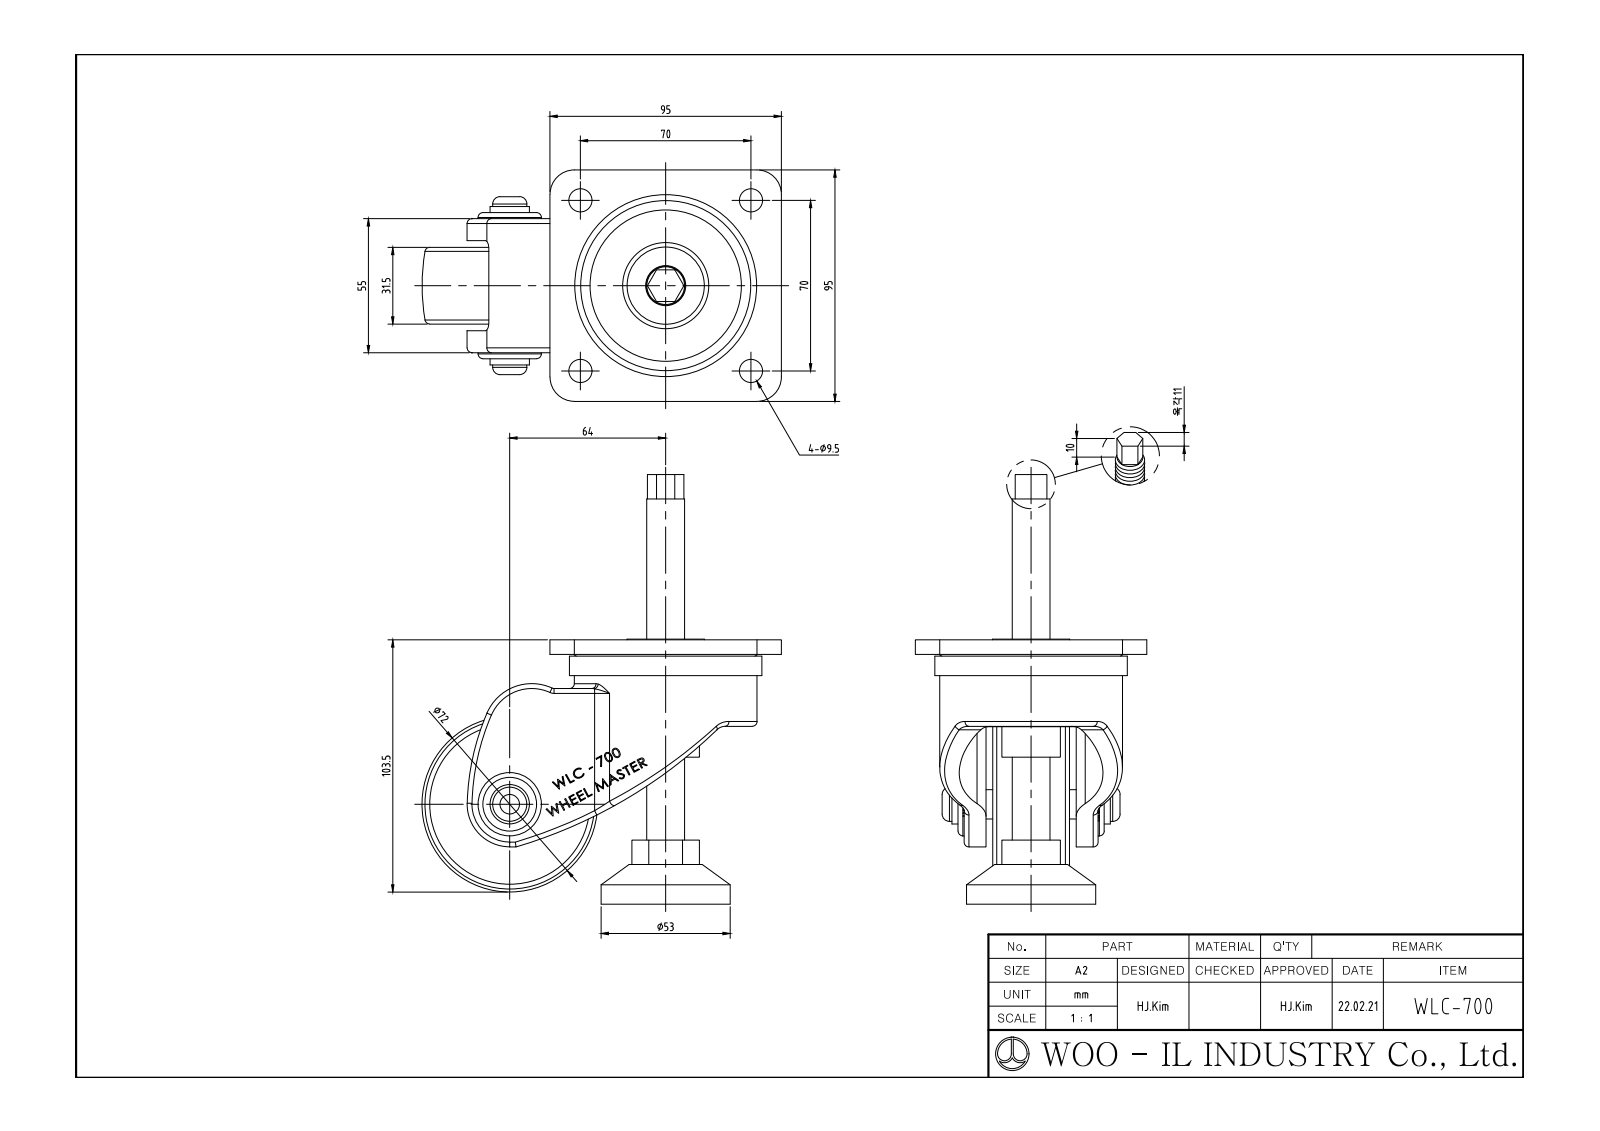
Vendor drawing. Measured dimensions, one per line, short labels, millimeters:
name: WLC-700F
written by: SolidWorks 2019 (AUTOMOTIVE_DESIGN)
unit: mm
bodies: 1 solid, 577 faces (3 planar, 6 cylindrical, 568 other)
size: 176.3 × 147.5 × 95
volume: 441 014 mm³; area: 79 003 mm²
bosses: 1× ⌀79, 1× ⌀38.1, 1× ⌀31.7
face distances: 35.96, 7.16, 28.8
